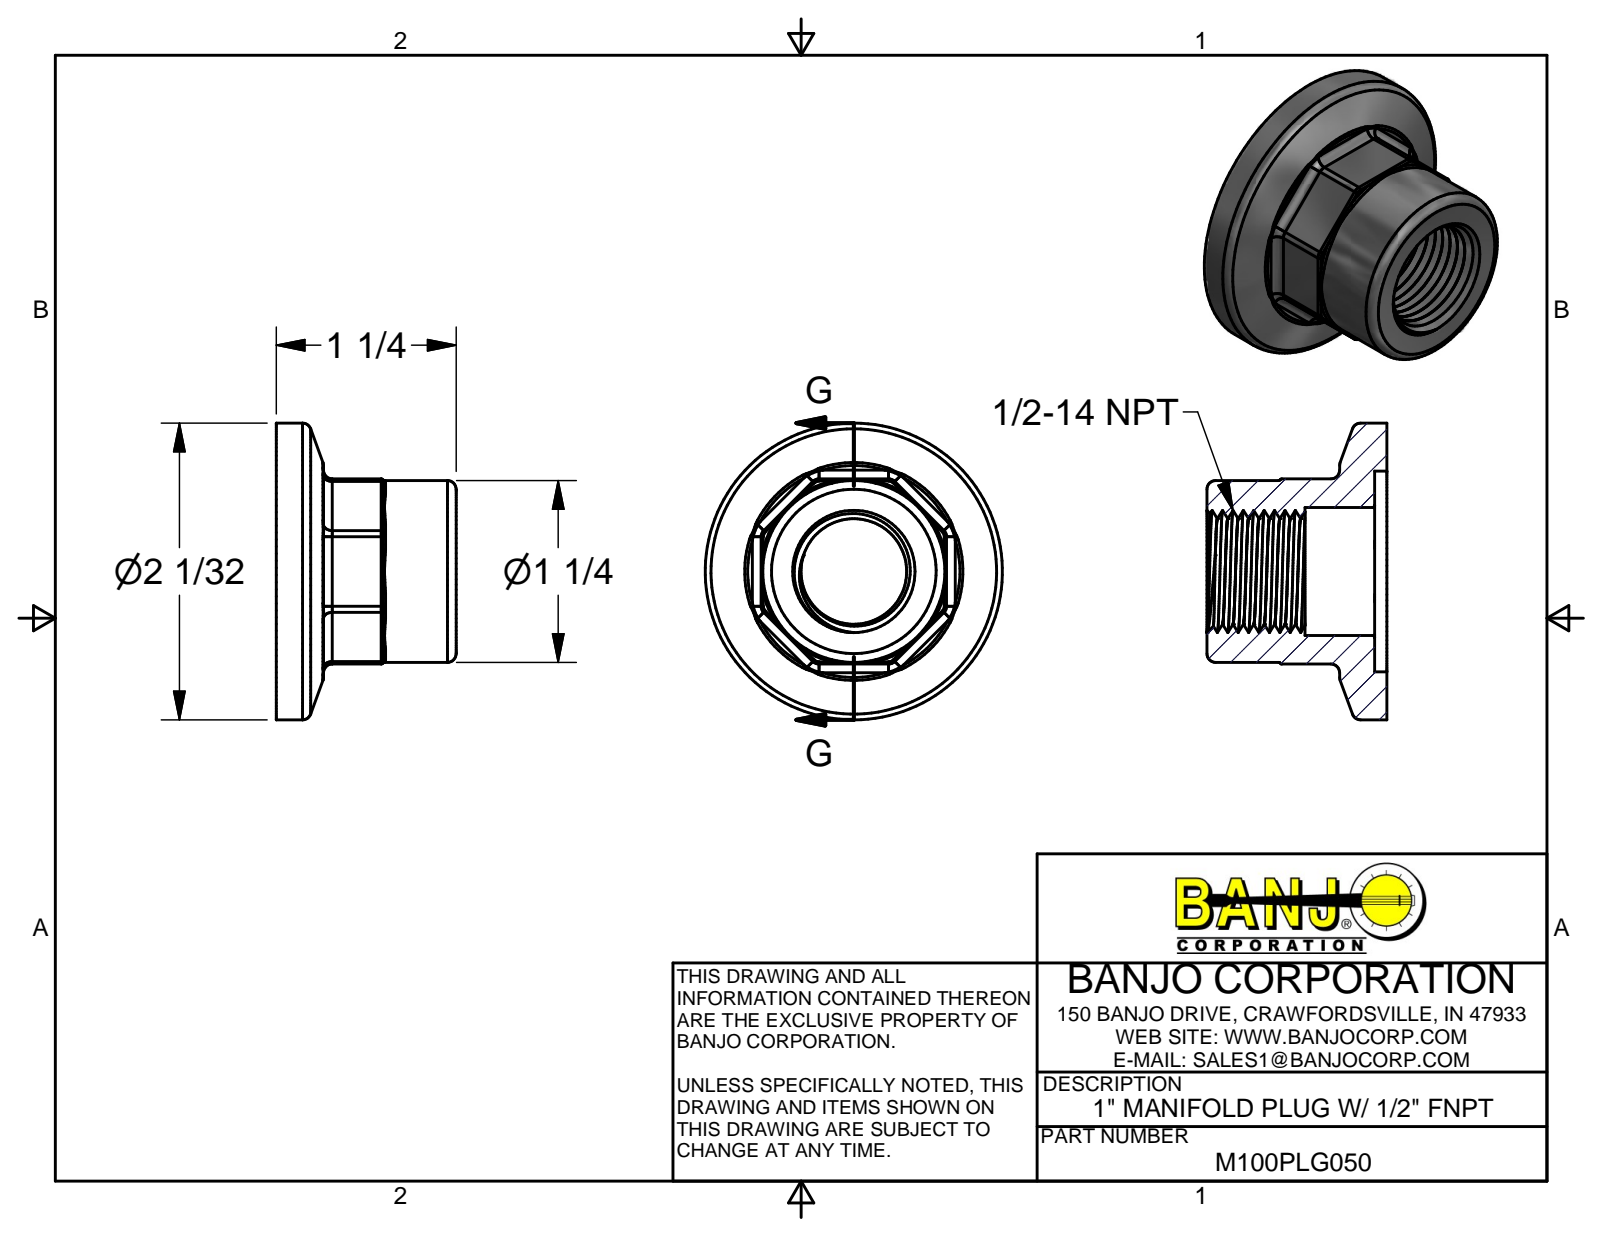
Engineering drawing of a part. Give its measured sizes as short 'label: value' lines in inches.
name: M100PLG050
written by: Autodesk Inventor 2013 (AUTOMOTIVE_DESIGN)
unit: in
bodies: 1 solid, 157 faces (36 planar, 43 cylindrical, 78 other)
size: 2.04 × 2.04 × 1.235
volume: 1.381 in³; area: 15.21 in²
holes: 1× ⌀1.38
bosses: 1× ⌀2.04, 1× ⌀1.25
rounds: 24× R0.06, 16× R0.015
face distances: 0.196, 0.084, 1.076, 1.077, 1.151, 1.235, 1.272, 1.273, 0.88, 0.88
